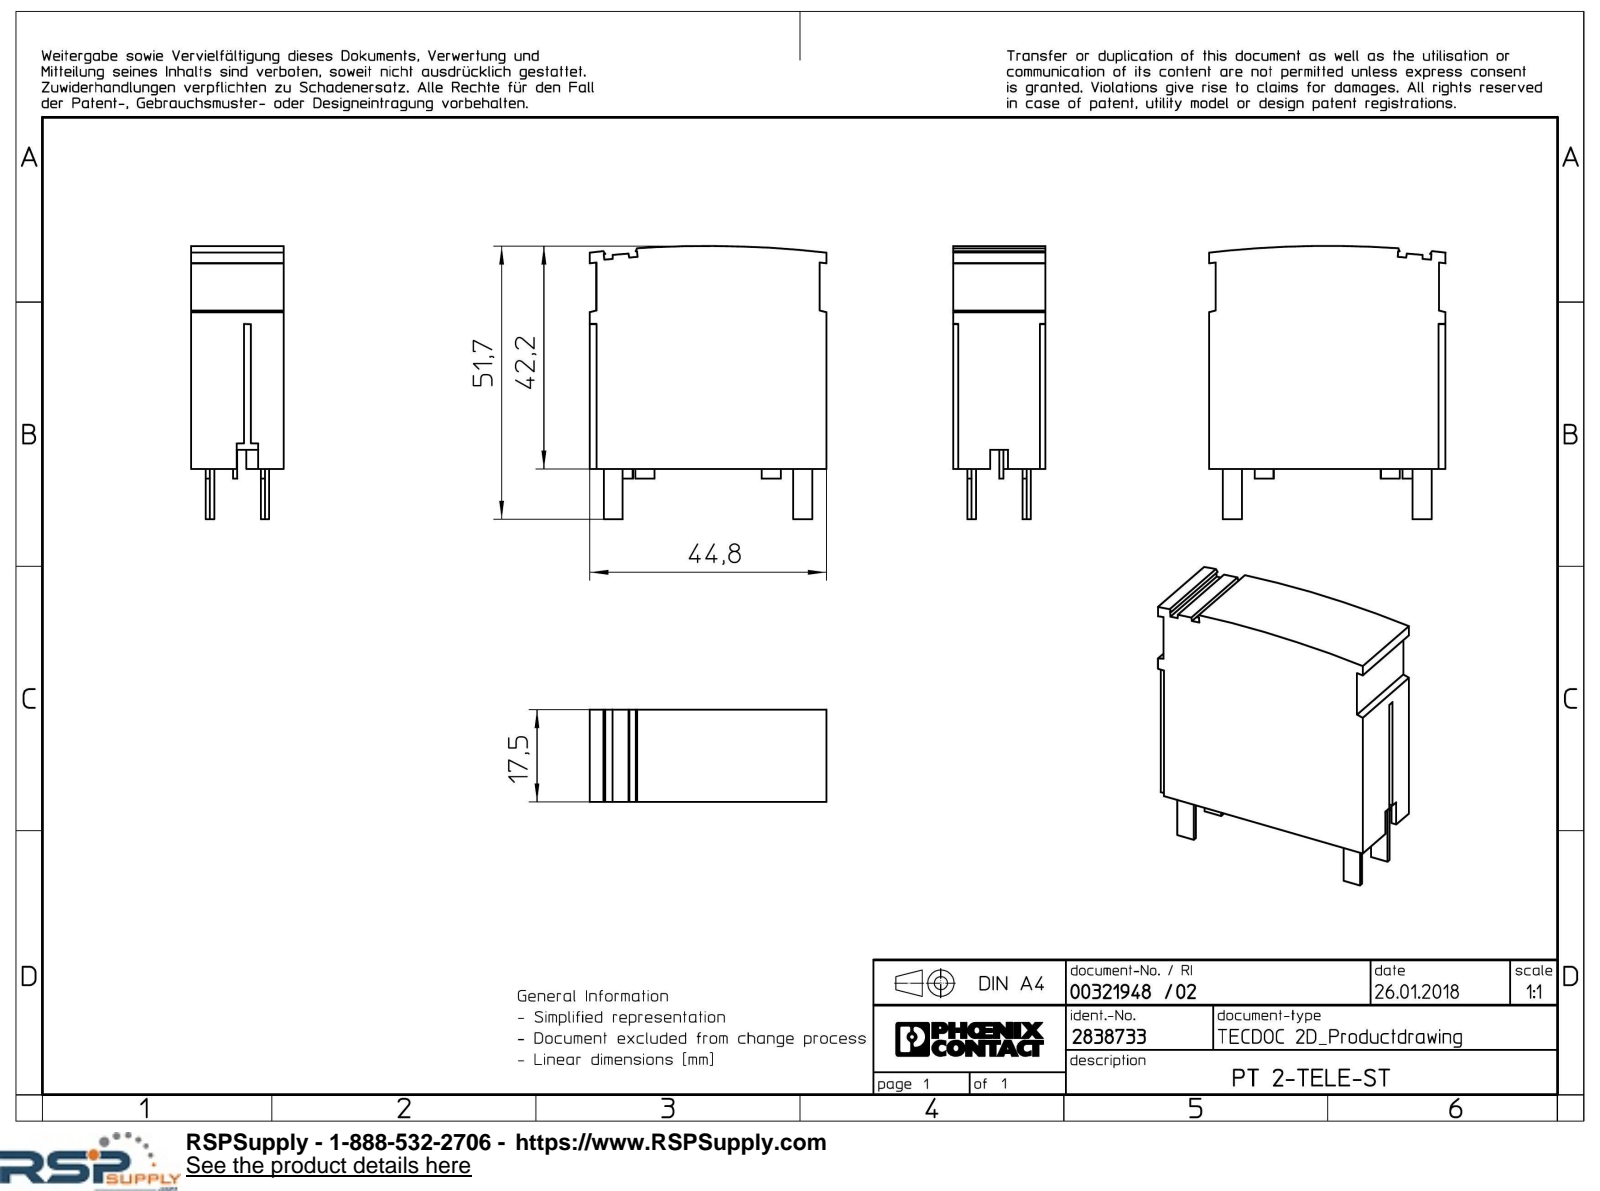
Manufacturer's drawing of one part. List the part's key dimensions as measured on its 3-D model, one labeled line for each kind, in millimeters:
Part name (STEP PRODUCT): PT_5...ST-select
STEP written by: Creo Elements/Direct Modeling 18.1I 14-Aug-2016 (C) Parametric Technology GmbH (AUTOMOTIVE_DESIGN)
Units: millimetres
Bodies: 1 solid, 107 faces (103 planar, 4 cylindrical, 0 other)
Overall size (bounding box): 51.7 × 44.8 × 17.5
Volume: 29 475 mm³ · Surface area: 8 181 mm²
Partial cylindrical surfaces — rounded edges, fillets, slot ends (radius × count): R198 ×1, R200 ×1
Main face-to-face distances: 17.5, 44.8, 1.25, 43.55, 0.7, 16.8, 0.8, 3.55, 13.95, 2.85
